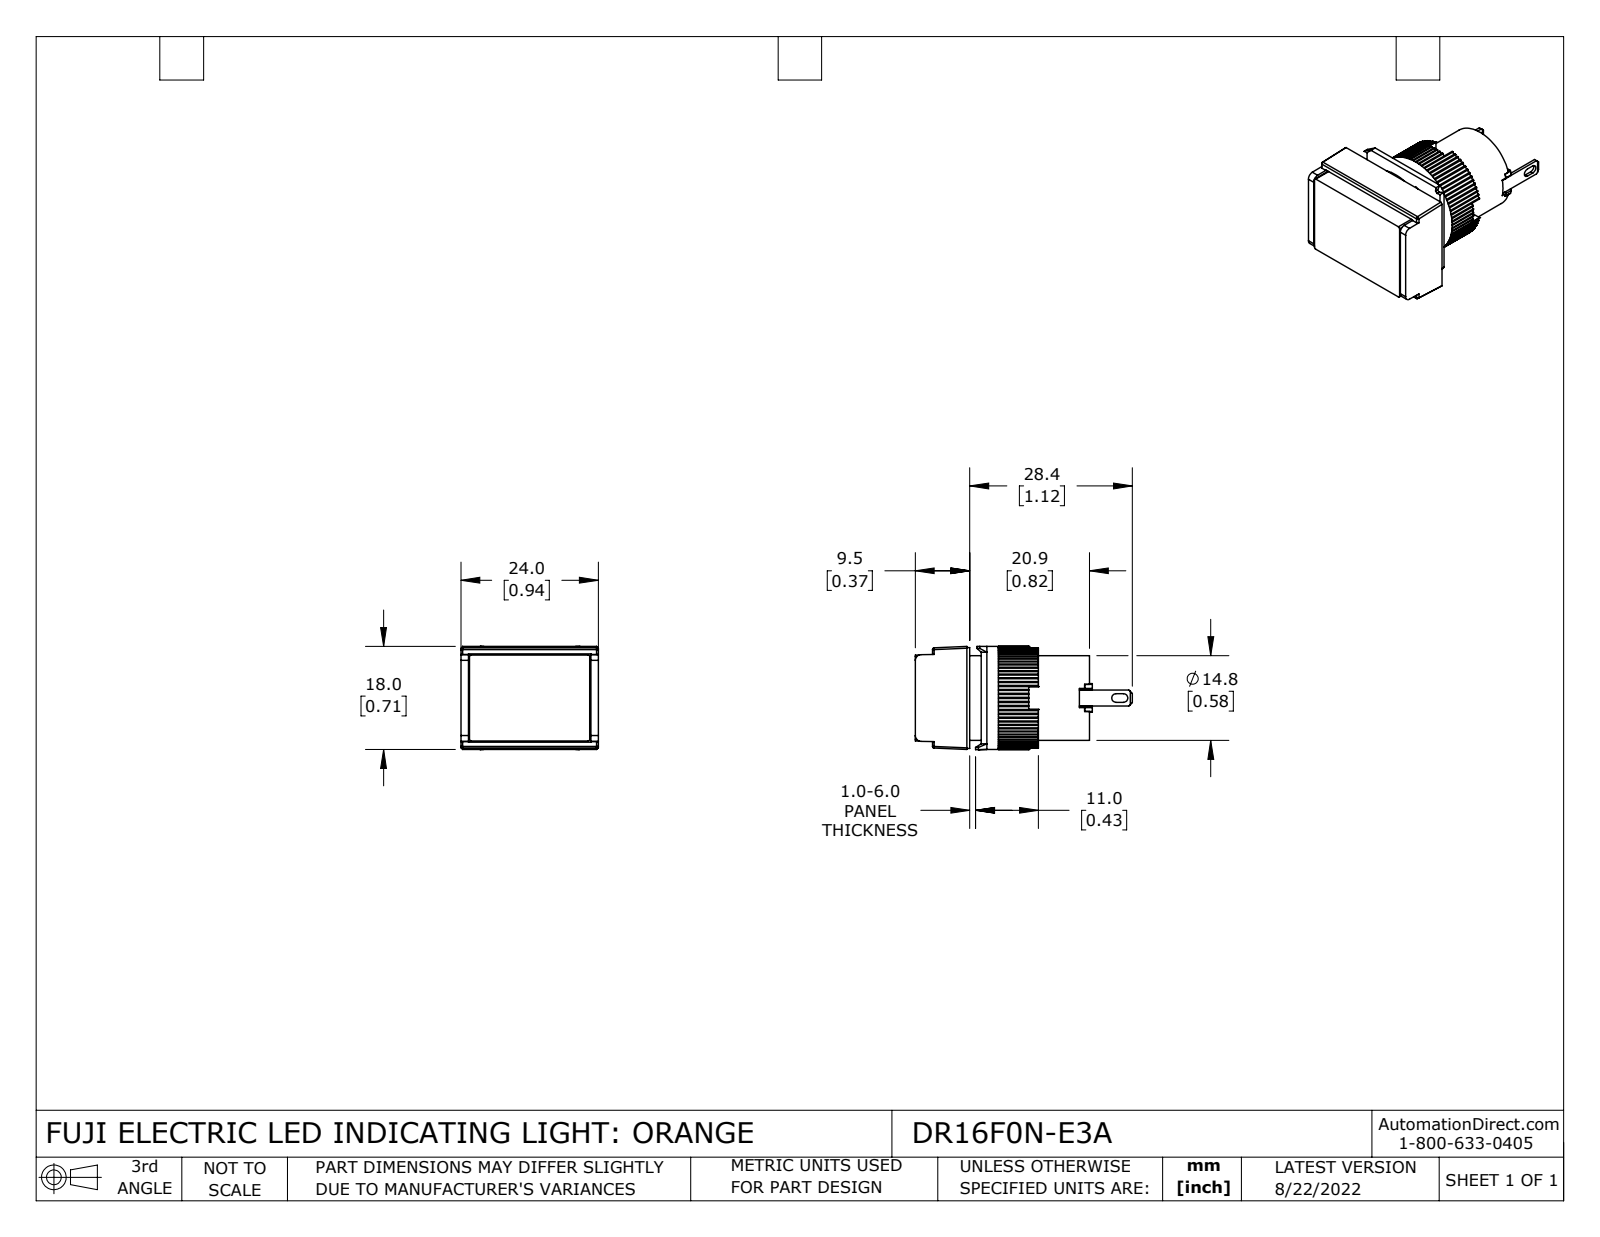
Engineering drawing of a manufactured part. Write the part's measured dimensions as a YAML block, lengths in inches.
part_name: "DR16F0N-E3A"
step_written_by: "SolidWorks 2021 (CONFIG_CONTROL_DESIGN)"
units: inches
bodies: {solids: 10, faces: 501, planar: 322, cylindrical: 175, other: 4}
overall_size: [1.492, 0.945, 0.709]
volume: 0.448
surface_area: 8.955
round_holes:
  - {diameter: 0.543, count: 1}
  - {diameter: 0.583, count: 1}
round_bosses_or_shafts:
  - {diameter: 0.709, count: 1}
  - {diameter: 0.693, count: 1}
partial_cylinders:
  - {radius: 0.01, count: 80}
  - {radius: 0.008, count: 8}
  - {radius: 0.012, count: 6}
  - {radius: 0.03, count: 2}
  - {radius: 0.039, count: 2}
face_to_face_distances: [0.213, 0.354, 0.142, 0.35, 0.492, 0.138, 0.843, 0.705, 0.453, 0.059]
